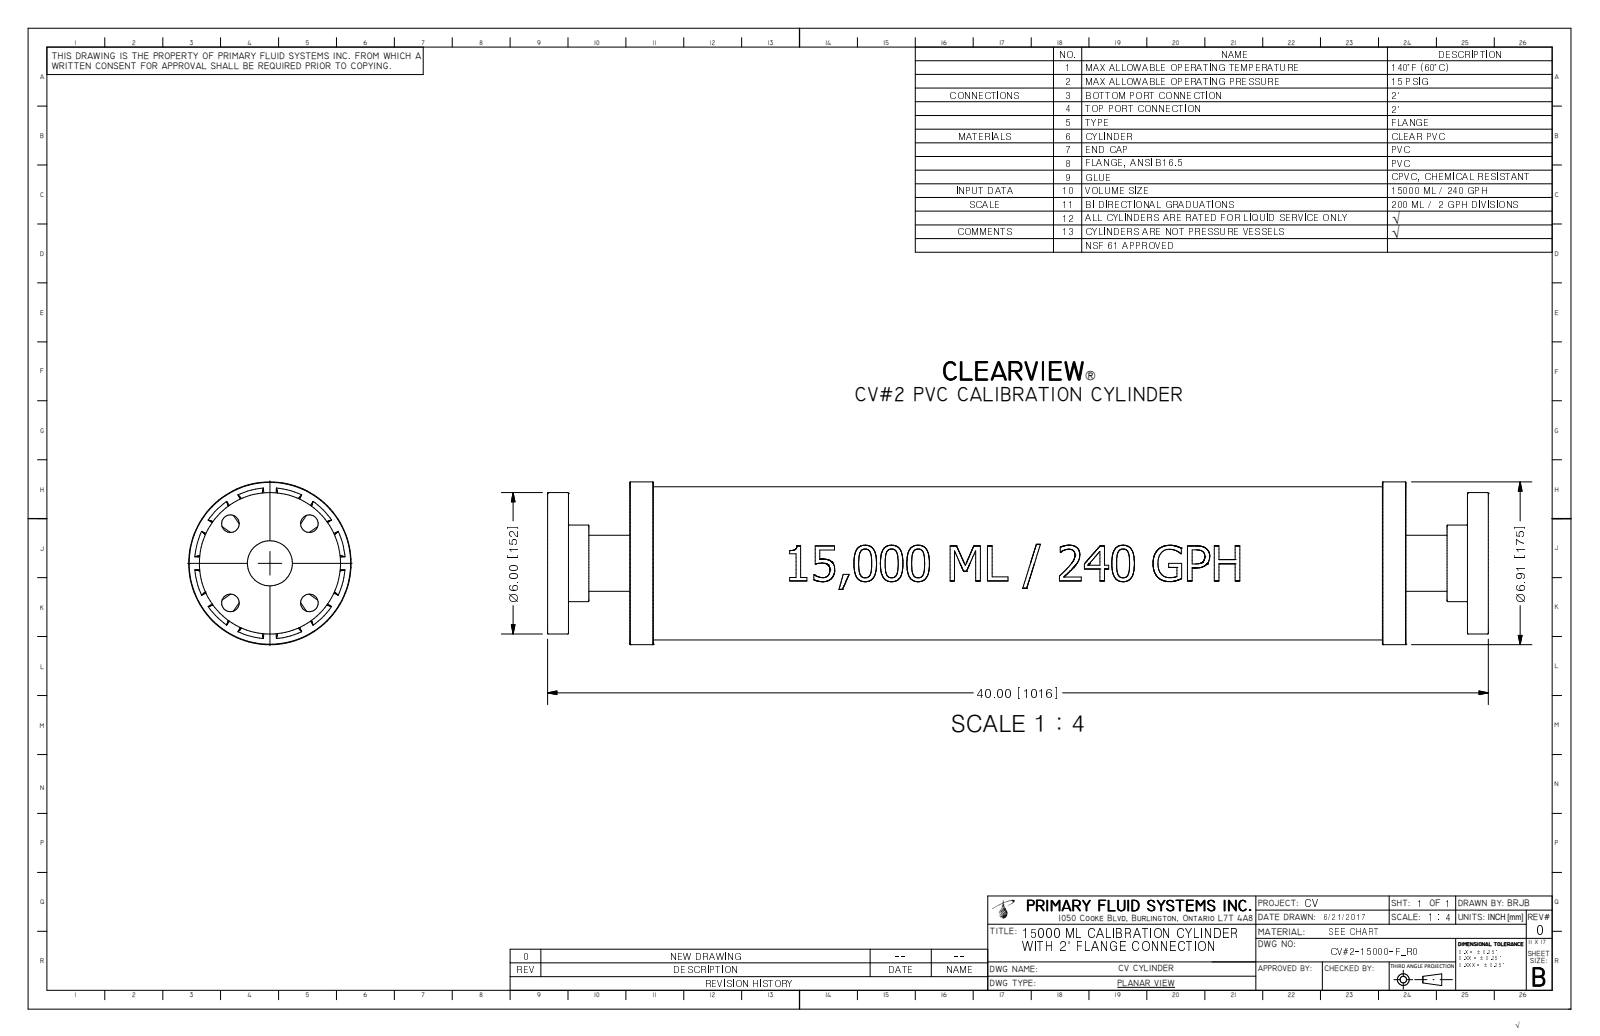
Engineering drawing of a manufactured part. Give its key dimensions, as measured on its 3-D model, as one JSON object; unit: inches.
{"part_name": "PV#2-15000-F_R0", "step_written_by": "Autodesk Inventor 2009 (AUTOMOTIVE_DESIGN)", "units": "inches", "bodies": {"solids": 1, "faces": 437, "planar": 141, "cylindrical": 45, "other": 251}, "overall_size": [40, 6.906, 6.906], "volume_in3": 165.6, "surface_area_in2": 1832, "round_holes": [[0.745, 4], [1.913, 1], [1.939, 1], [6.32, 1]], "round_bosses_or_shafts": [[6.906, 1], [6.5, 1], [6, 1], [3.244, 1], [2.375, 1]], "partial_cylinders_radius": [[3.249, 1]], "face_to_face_distances": [0.885, 39.115, 40, 38.23, 4, 36, 3.115, 35.115, 1.755, 38.245], "hole_center_spacings": [2.375, 3.359, 4.75]}
